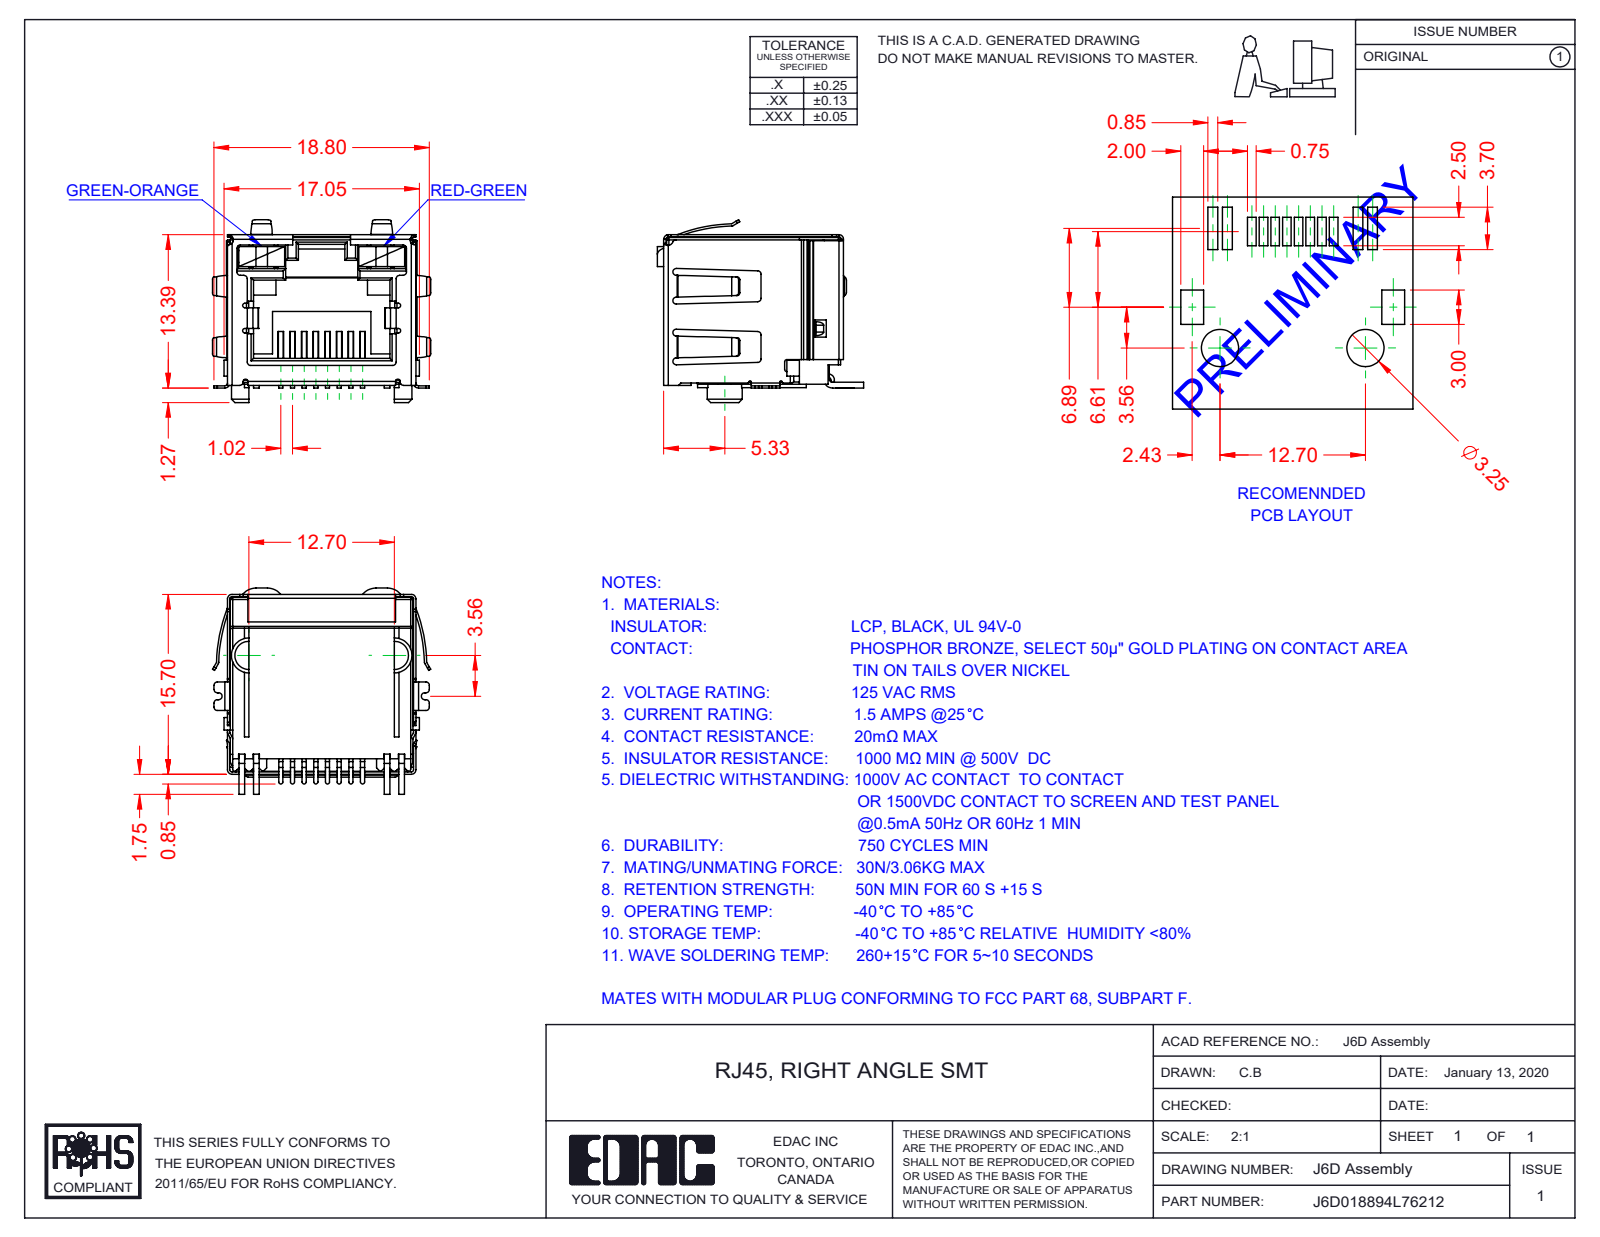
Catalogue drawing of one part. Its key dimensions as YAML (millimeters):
part_name: "6D Shield_LED - EMI; 6D Contacts; J6D018894L76212; 6D LED RH_6-Red-Green (+2 more)"
step_written_by: "SolidWorks 2016 (CONFIG_CONTROL_DESIGN)"
units: millimeters
bodies: {solids: 12, faces: 1034, planar: 703, cylindrical: 286, other: 45}
overall_size: [19.06, 18, 15.95]
volume: 1790
surface_area: 4796
partial_cylinders:
  - {radius: 0.3, count: 55}
  - {radius: 0.2, count: 40}
  - {radius: 0.4, count: 19}
  - {radius: 0.25, count: 16}
  - {radius: 0.1, count: 12}
  - {radius: 0.15, count: 8}
  - {radius: 0.18, count: 8}
  - {radius: 0.5, count: 6}
face_to_face_distances: [16, 16.2, 16.25, 2.25, 1, 15.95, 12.8, 0.45, 13.05, 10.6]
